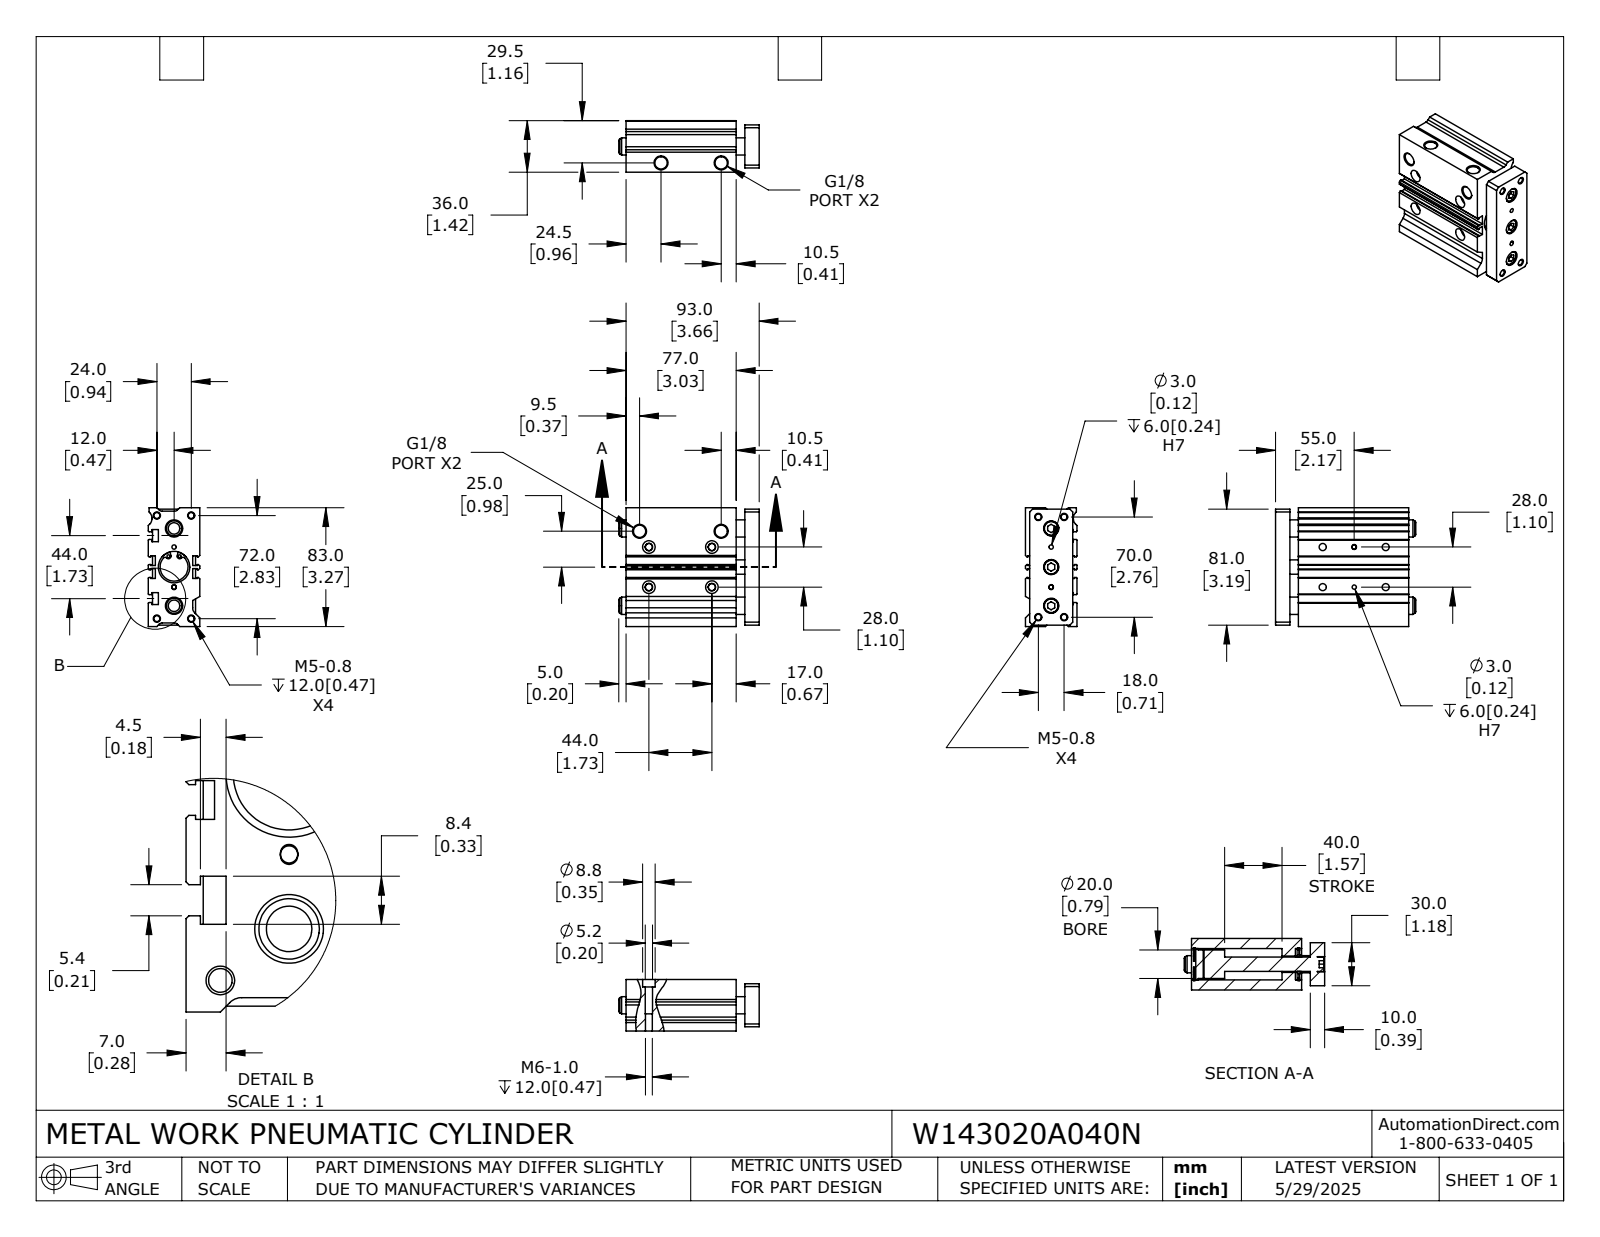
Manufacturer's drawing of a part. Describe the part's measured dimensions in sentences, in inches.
The part is named "W143020A040N; W143020A040N_BODY; W143020A040N_ROD". Its 3-D file was written by "SolidWorks 2024 (CONFIG_CONTROL_DESIGN)". It is 6 solids with 357 faces: 174 planar, 145 cylindrical and 38 other. Overall it measures 3.858 by 3.268 by 1.417 inches. Its volume is 12.58 cubic inches and its surface area 102.9 square inches. Round holes: 8 of diameter 0.163, 4 of diameter 0.079, 4 of diameter 0.118, 4 of diameter 0.205, 4 of diameter 0.337, 4 of diameter 0.346, 3 of diameter 0.413, 2 of diameter 0.194, 2 of diameter 0.194, 2 of diameter 0.472, 1 of diameter 0.449, 1 of diameter 0.767. Round bosses or shafts: 3 of diameter 0.394, 2 of diameter 0.906, 1 of diameter 0.787, 1 of diameter 0.512. Partial cylindrical surfaces (rounded edges, fillets, slot ends): 4 of radius 0.053, 4 of radius 0.059, 4 of radius 0.071, 4 of radius 0.118, 3 of radius 0.197. The main face-to-face distances are 1.417, 3.268, 0.098, 0.079, 0.197, 1.22, 0.394, 0.236, 0.63, 0.118. The hole center spacings are 0.124, 0.296, 0.336, 0.474, 0.591, 0.78, 0.828, 0.864.
